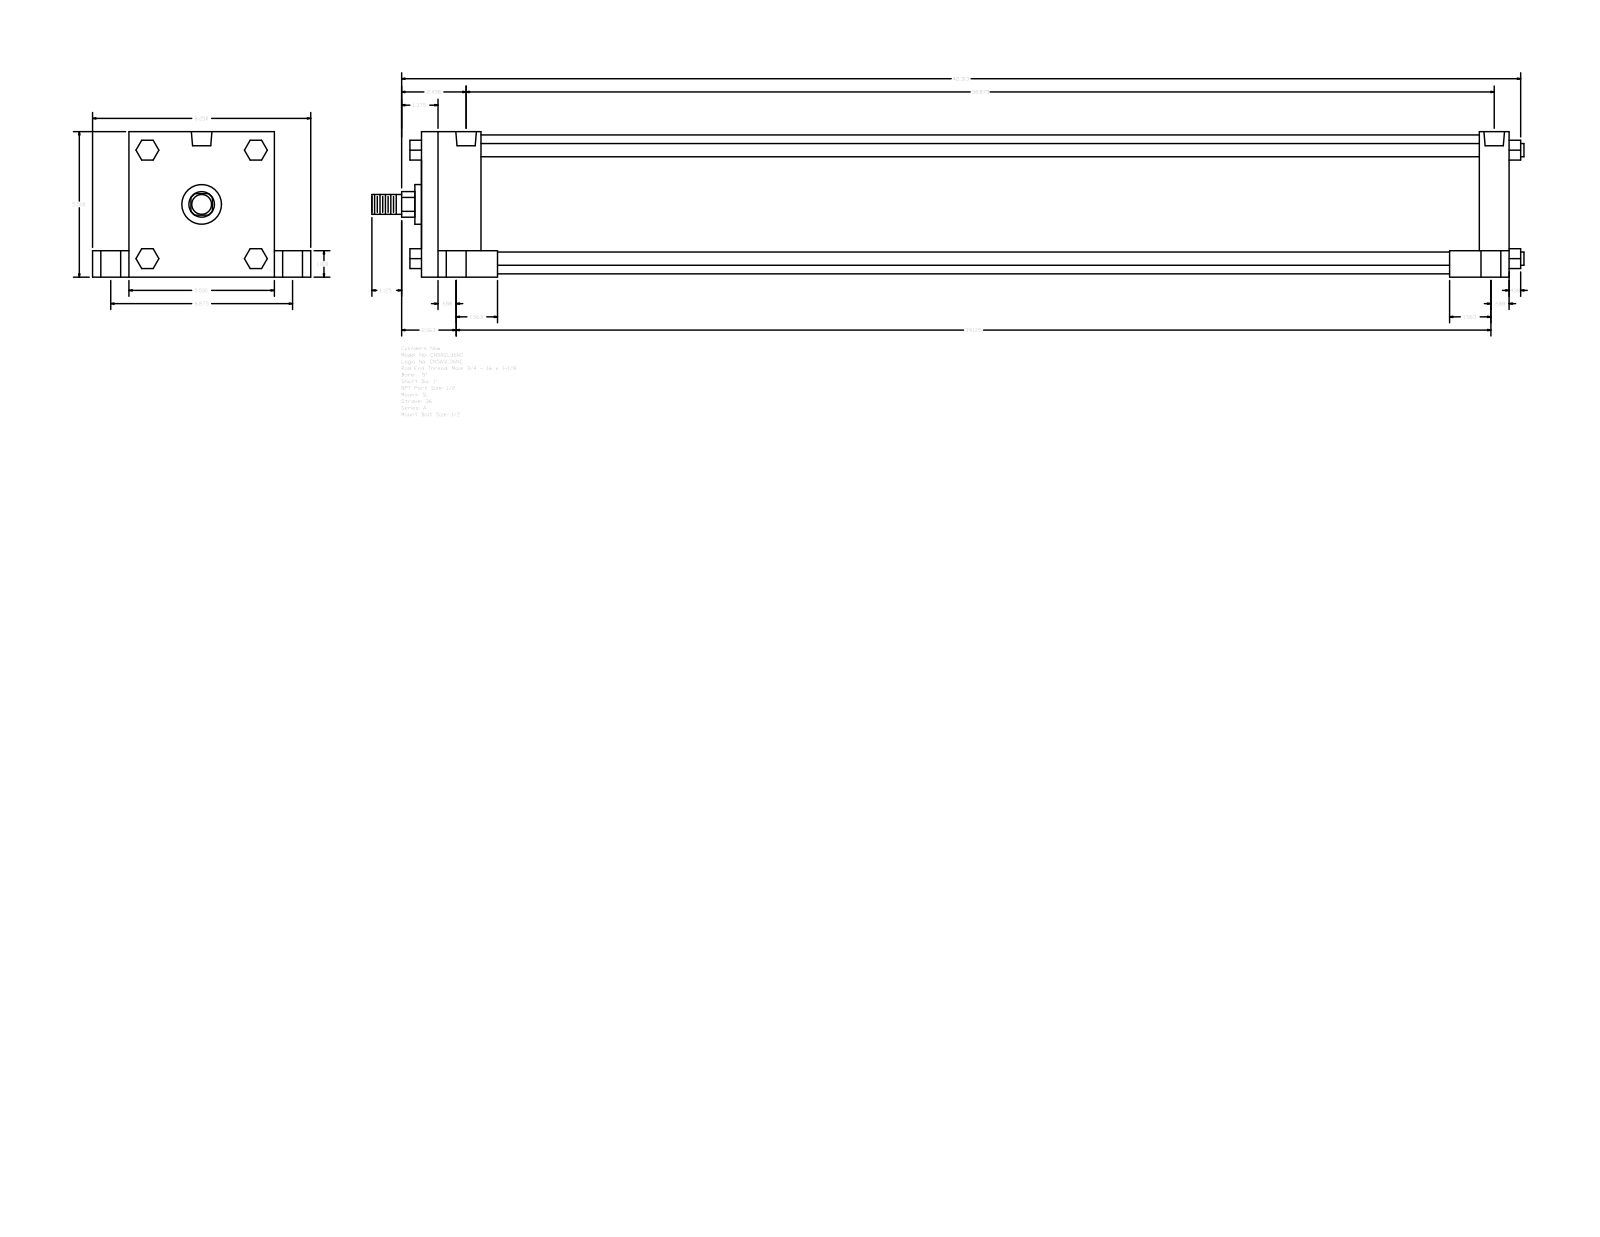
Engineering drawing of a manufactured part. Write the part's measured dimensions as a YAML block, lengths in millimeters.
part_name: "A_SL__0500_1"
step_written_by: "GSSL Pune (CONFIG_CONTROL_DESIGN)"
units: millimeters
bodies: {solids: 0, faces: 150, planar: 114, cylindrical: 36, other: 0}
overall_size: [1106.49, 209.55, 139.7]
round_holes:
  - {diameter: 8.73, count: 4}
  - {diameter: 19.05, count: 4}
  - {diameter: 25.4, count: 4}
  - {diameter: 19.77, count: 2}
round_bosses_or_shafts:
  - {diameter: 12.7, count: 4}
  - {diameter: 133.35, count: 1}
  - {diameter: 38.1, count: 1}
  - {diameter: 25.4, count: 1}
  - {diameter: 19.05, count: 1}
partial_cylinders:
  - {radius: 12.29, count: 1}
face_to_face_distances: [139.7, 1044.57, 28.57, 25.4, 114.3, 34.93, 174.63, 57.15, 1016, 958.85]
hole_center_spacings: [2.39, 87.31, 87.37, 87.83, 88.12, 174.62, 982.65, 985.04]
